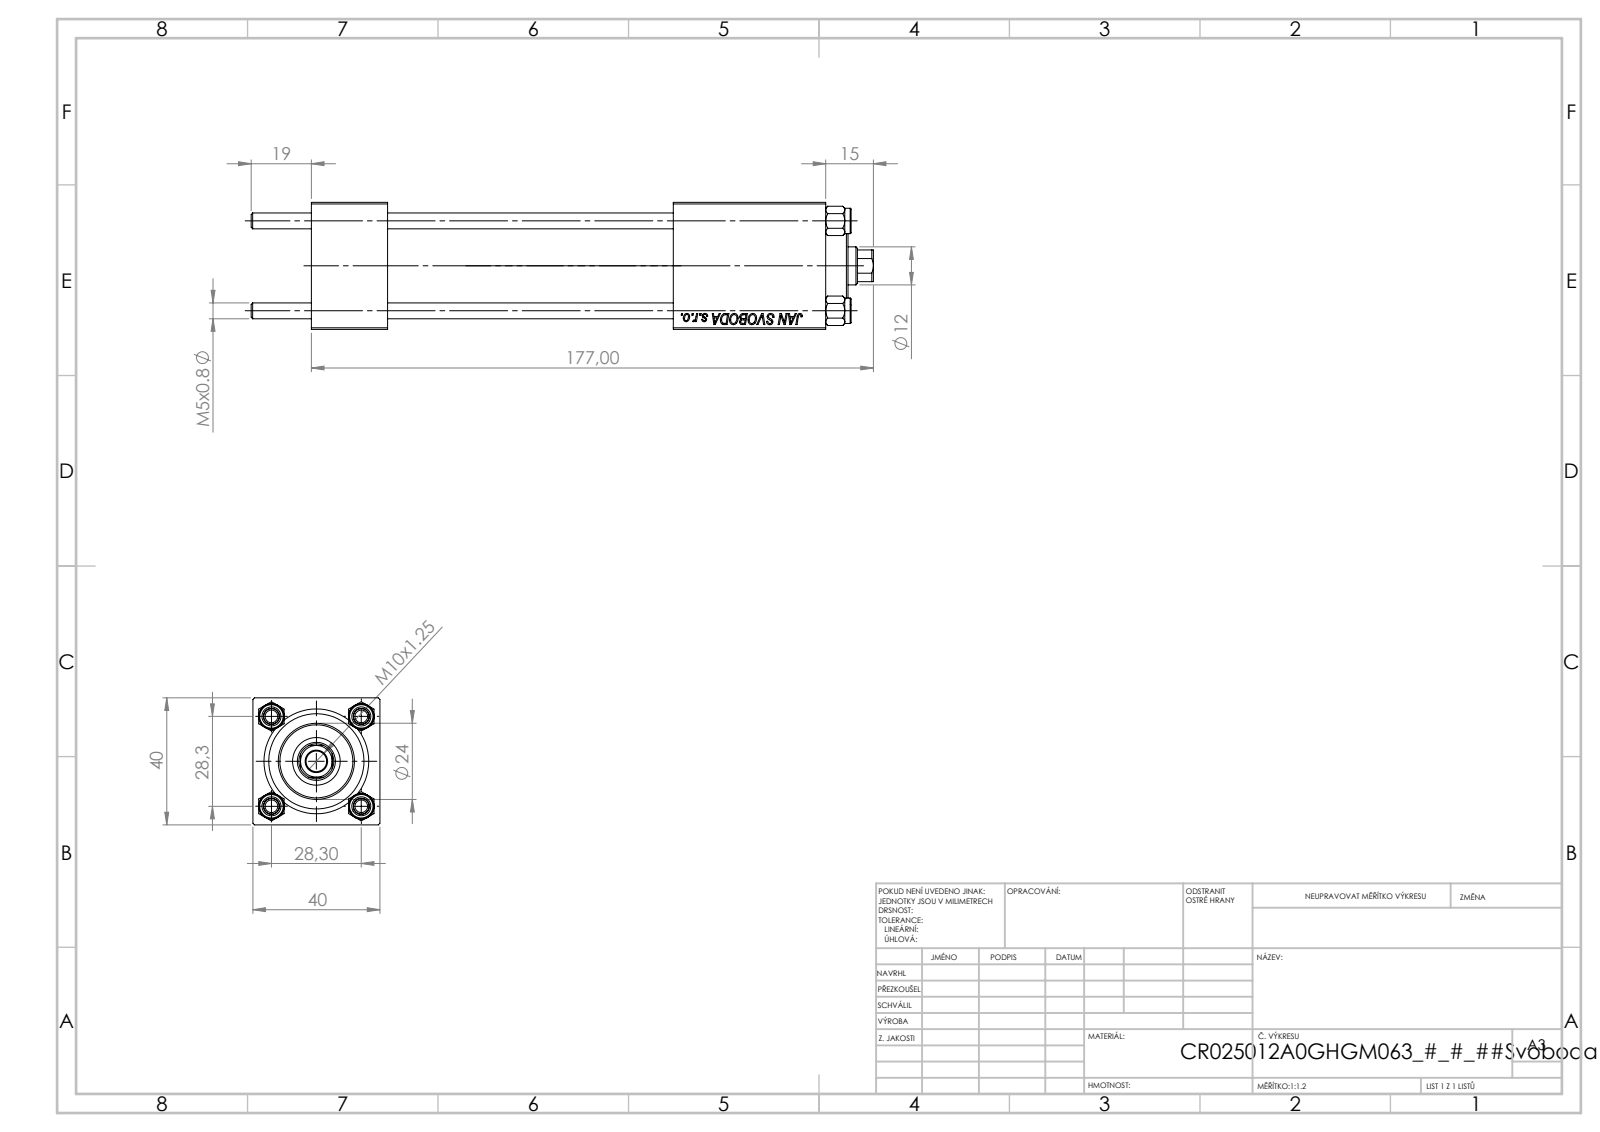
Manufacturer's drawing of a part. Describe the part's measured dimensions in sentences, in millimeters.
The part is named "CR025_012_A_0_G_A_G_M_020_+#_##_TYCINKA; V215CR_BODY_A; NUT_M5; V215_VC_A (+1 more)". Its 3-D file was written by "SolidWorks 2019 (CONFIG_CONTROL_DESIGN)". It is 11 solids with 1131 faces: 517 planar, 78 cylindrical and 536 other. Overall it measures 196 by 40 by 40 millimeters. Its volume is 164 412 cubic millimeters and its surface area 70 759 square millimeters. Round holes: 4 of diameter 5, 3 of diameter 20, 2 of diameter 7, 2 of diameter 13.16, 1 of diameter 6.5, 1 of diameter 12, 1 of diameter 15, 1 of diameter 25, 1 of diameter 30. Round bosses or shafts: 4 of diameter 8, 1 of diameter 31, 1 of diameter 24. Partial cylindrical surfaces (rounded edges, fillets, slot ends): 1 of radius 5.5. The main face-to-face distances are 40, 24, 162, 138, 133.3, 109.3, 28.7, 114, 90, 19.3. The hole center spacings are 20.01, 28.3, 40.02, 115.
